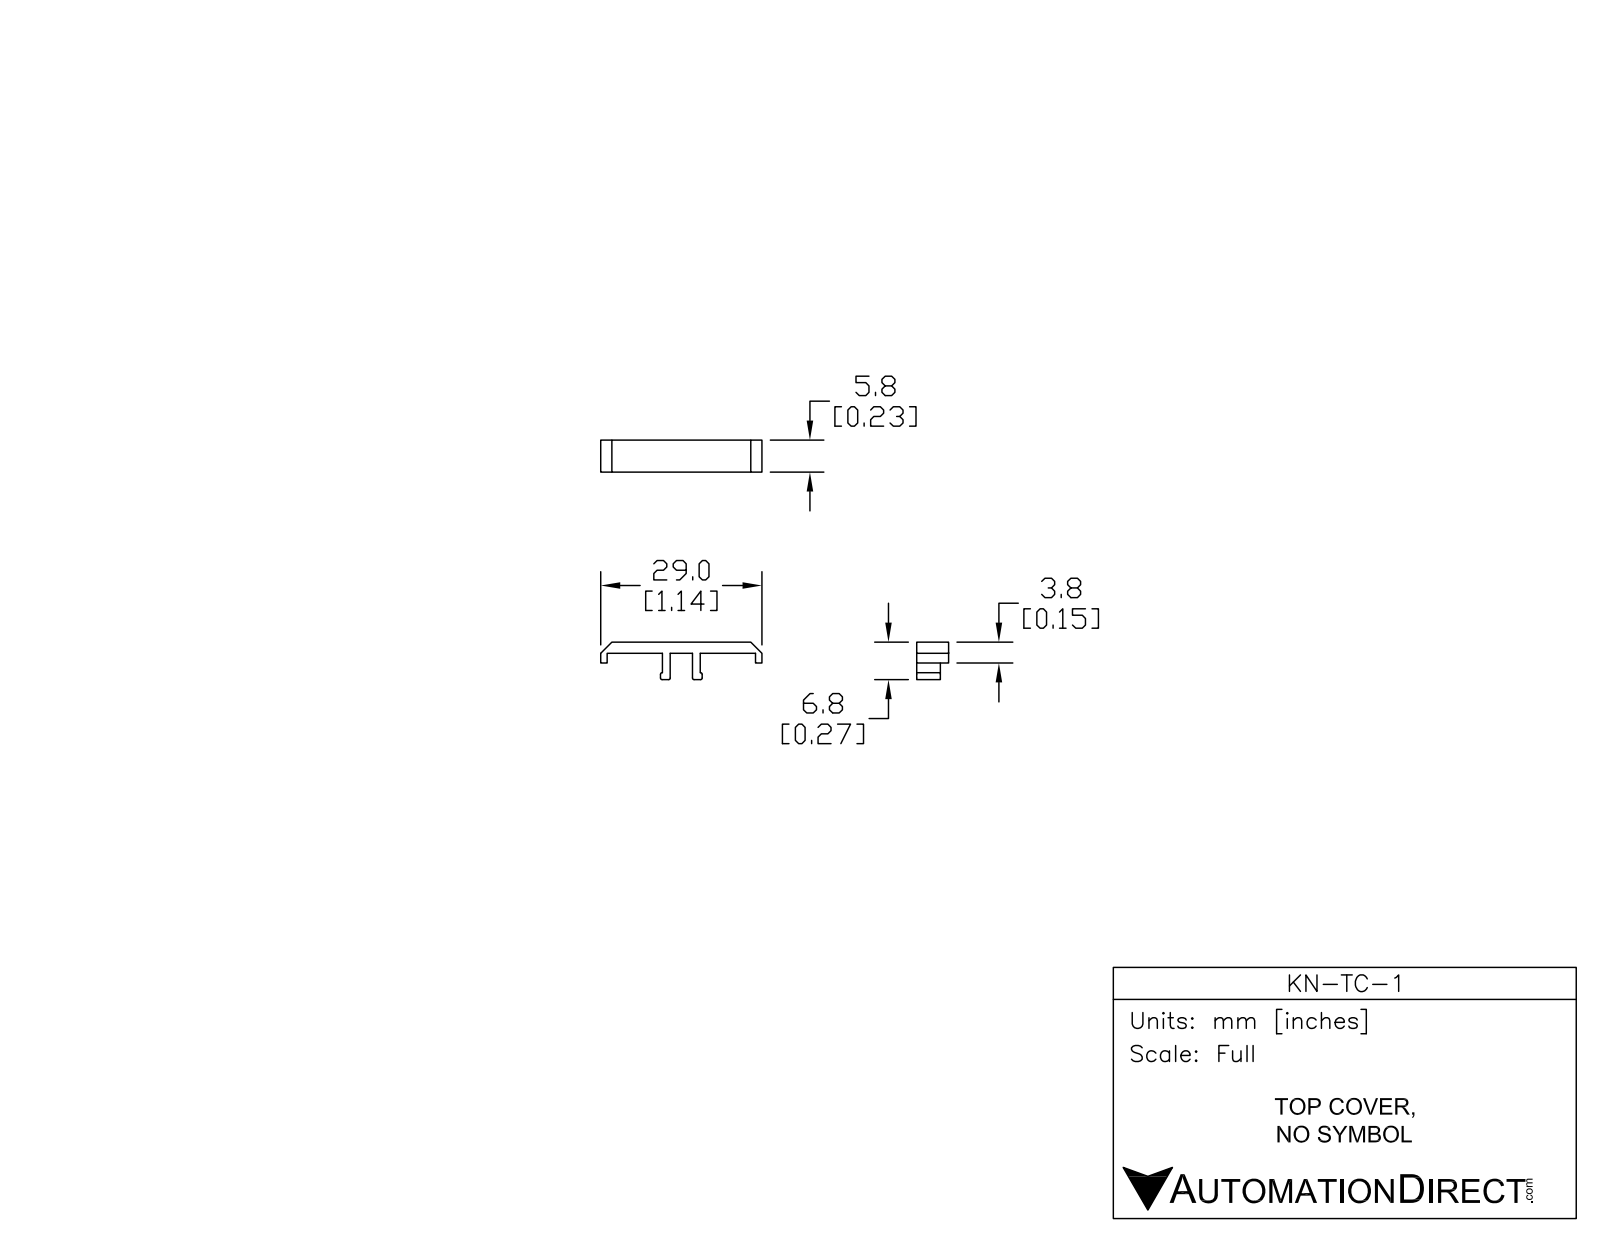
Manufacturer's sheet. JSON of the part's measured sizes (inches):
{"part_name": "KN-TC-1", "step_written_by": "SolidWorks 2014 (AUTOMOTIVE_DESIGN)", "units": "inches", "bodies": {"solids": 1, "faces": 30, "planar": 24, "cylindrical": 6, "other": 0}, "overall_size": [1.142, 0.266, 0.226], "volume_in3": 0.024, "surface_area_in2": 0.947, "partial_cylinders_radius": [[0.012, 6]], "face_to_face_distances": [0.079, 0.226, 0.055, 0.213, 0.437, 0.492, 0.65, 0.705, 0.045, 1.096]}
